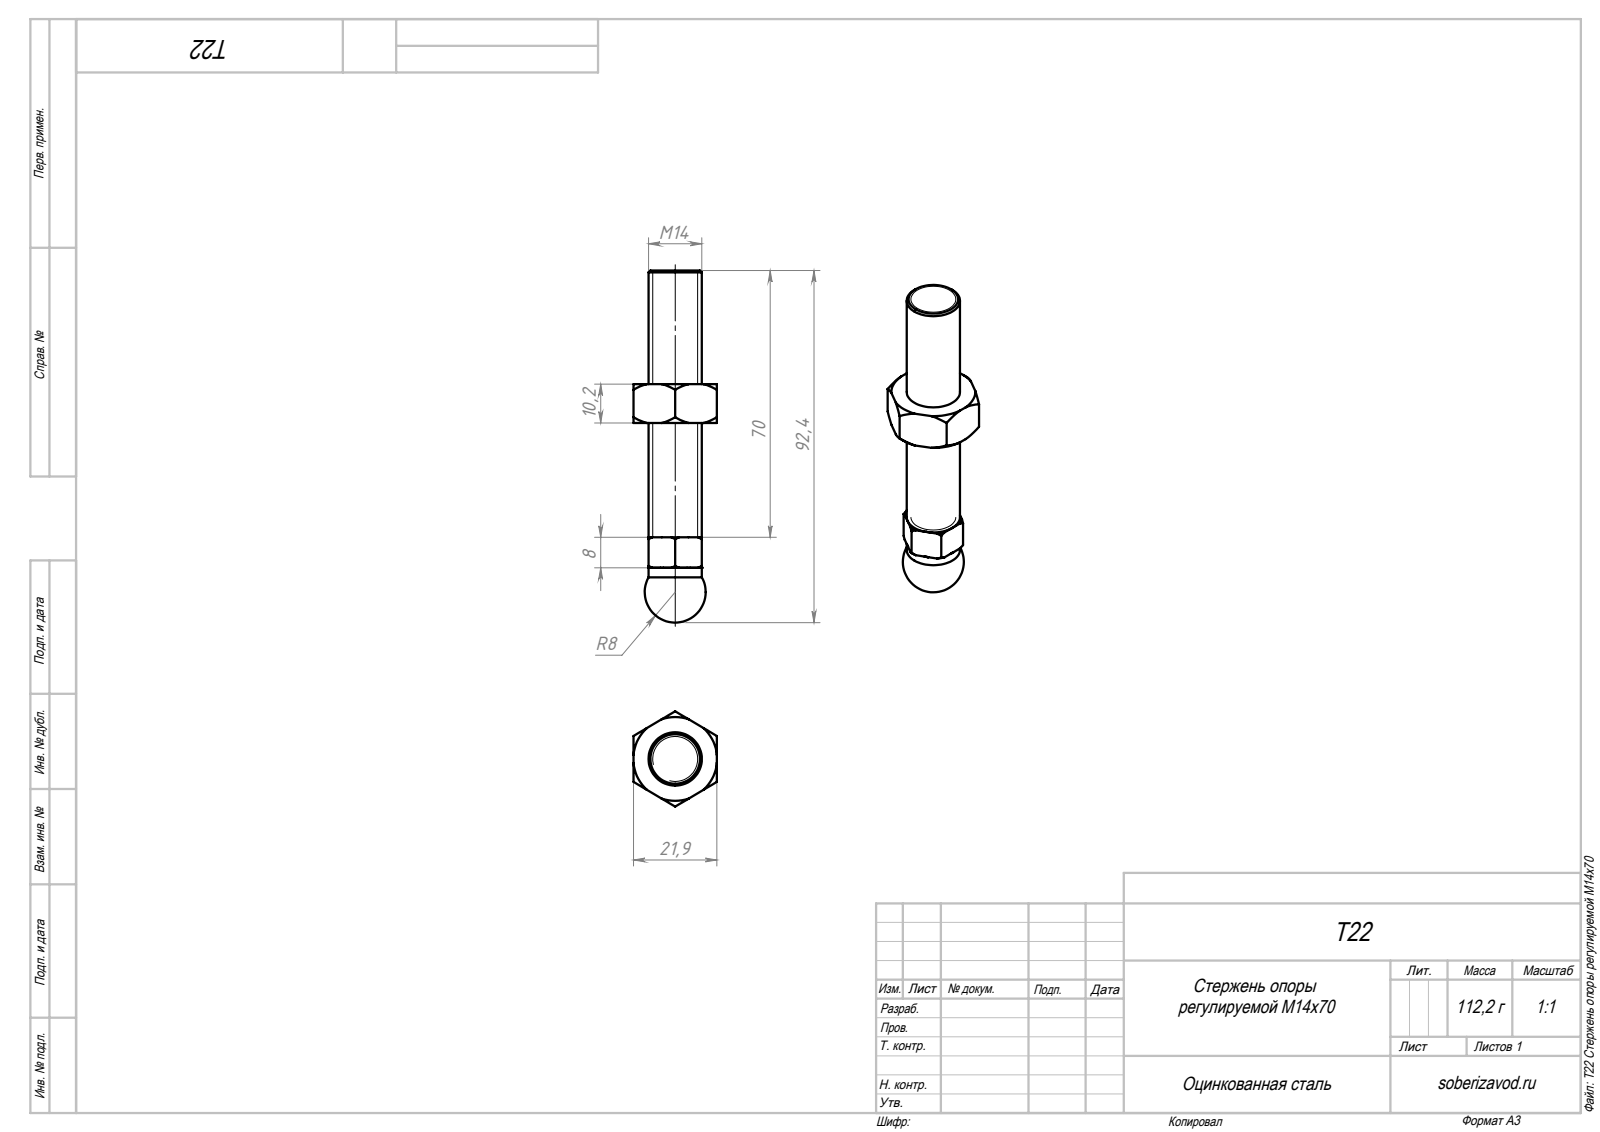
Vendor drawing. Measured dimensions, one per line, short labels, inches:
name: T22 Стержень опоры регулируемой М14х70
written by: SolidWorks 2018 (AUTOMOTIVE_DESIGN)
unit: in
bodies: 1 solid, 80 faces (36 planar, 6 cylindrical, 38 other)
size: 3.637 × 0.984 × 0.862
volume: 1.028 in³; area: 7.959 in²
bosses: 1× ⌀0.551
face distances: 0.847, 0.402, 0.551, 1.575, 1.173, 0.156, 0.707, 0.862, 1.181, 1.583
